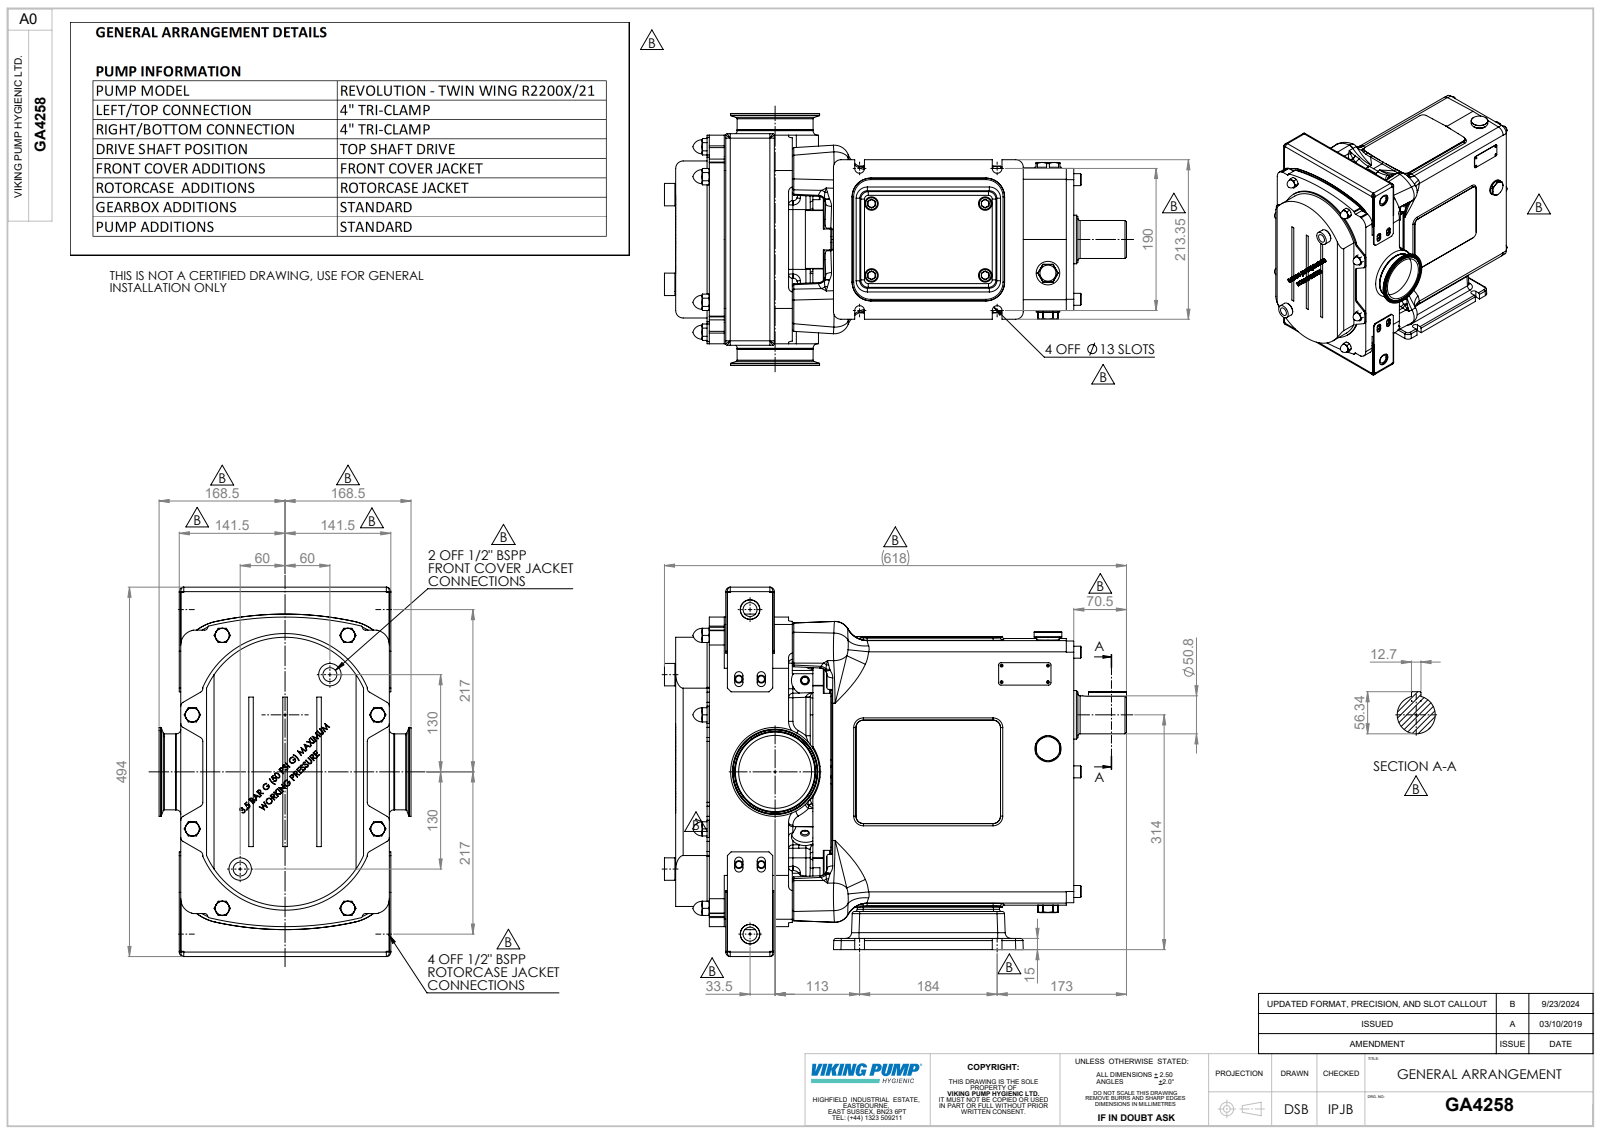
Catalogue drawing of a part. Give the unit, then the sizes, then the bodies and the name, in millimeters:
Units: millimetres
Overall size (bounding box): 618 × 494 × 337
Round holes (diameter × count): ⌀8.5 ×4, ⌀13.5 ×4, ⌀18.6 ×4, ⌀26.2 ×4, ⌀149 ×2, ⌀35 ×1, ⌀97.55 ×1
Round bosses / shafts (diameter × count): ⌀14 ×10, ⌀8 ×10, ⌀16 ×6, ⌀30 ×5, ⌀18 ×4, ⌀187 ×2, ⌀140 ×2, ⌀106 ×2
Partial cylindrical surfaces — rounded edges, fillets, slot ends (radius × count): R1 ×80, R6 ×72, R7 ×64, R3 ×44, R10 ×30, R0.2 ×24, R5 ×16, R4 ×14
Main face-to-face distances: 2, 45, 44.5, 234.5, 190, 41.5, 3, 487.5, 532.5, 193
Hole centre spacings: 94.2, 124, 196.55, 248, 341.33, 152.5, 30, 80.55
Volume: 43 140 000 mm³ · Surface area: 1 824 000 mm²
Bodies: 13 solids, 3007 faces (1139 planar, 813 cylindrical, 1055 other)
Part name (STEP PRODUCT): Copy of R2200 CPP H TSD 2^GA4258; Copy of R2200X^Copy of R2200 CPP H TSD 2_GA4258; Copy of Frame 5 Bolt on Jacket^GA4258; Copy of GEARBOX_TSD^Copy of R2200 CPP H TSD 2_GA4258 (+3 more)
STEP written by: SolidWorks 2023 (AUTOMOTIVE_DESIGN)
